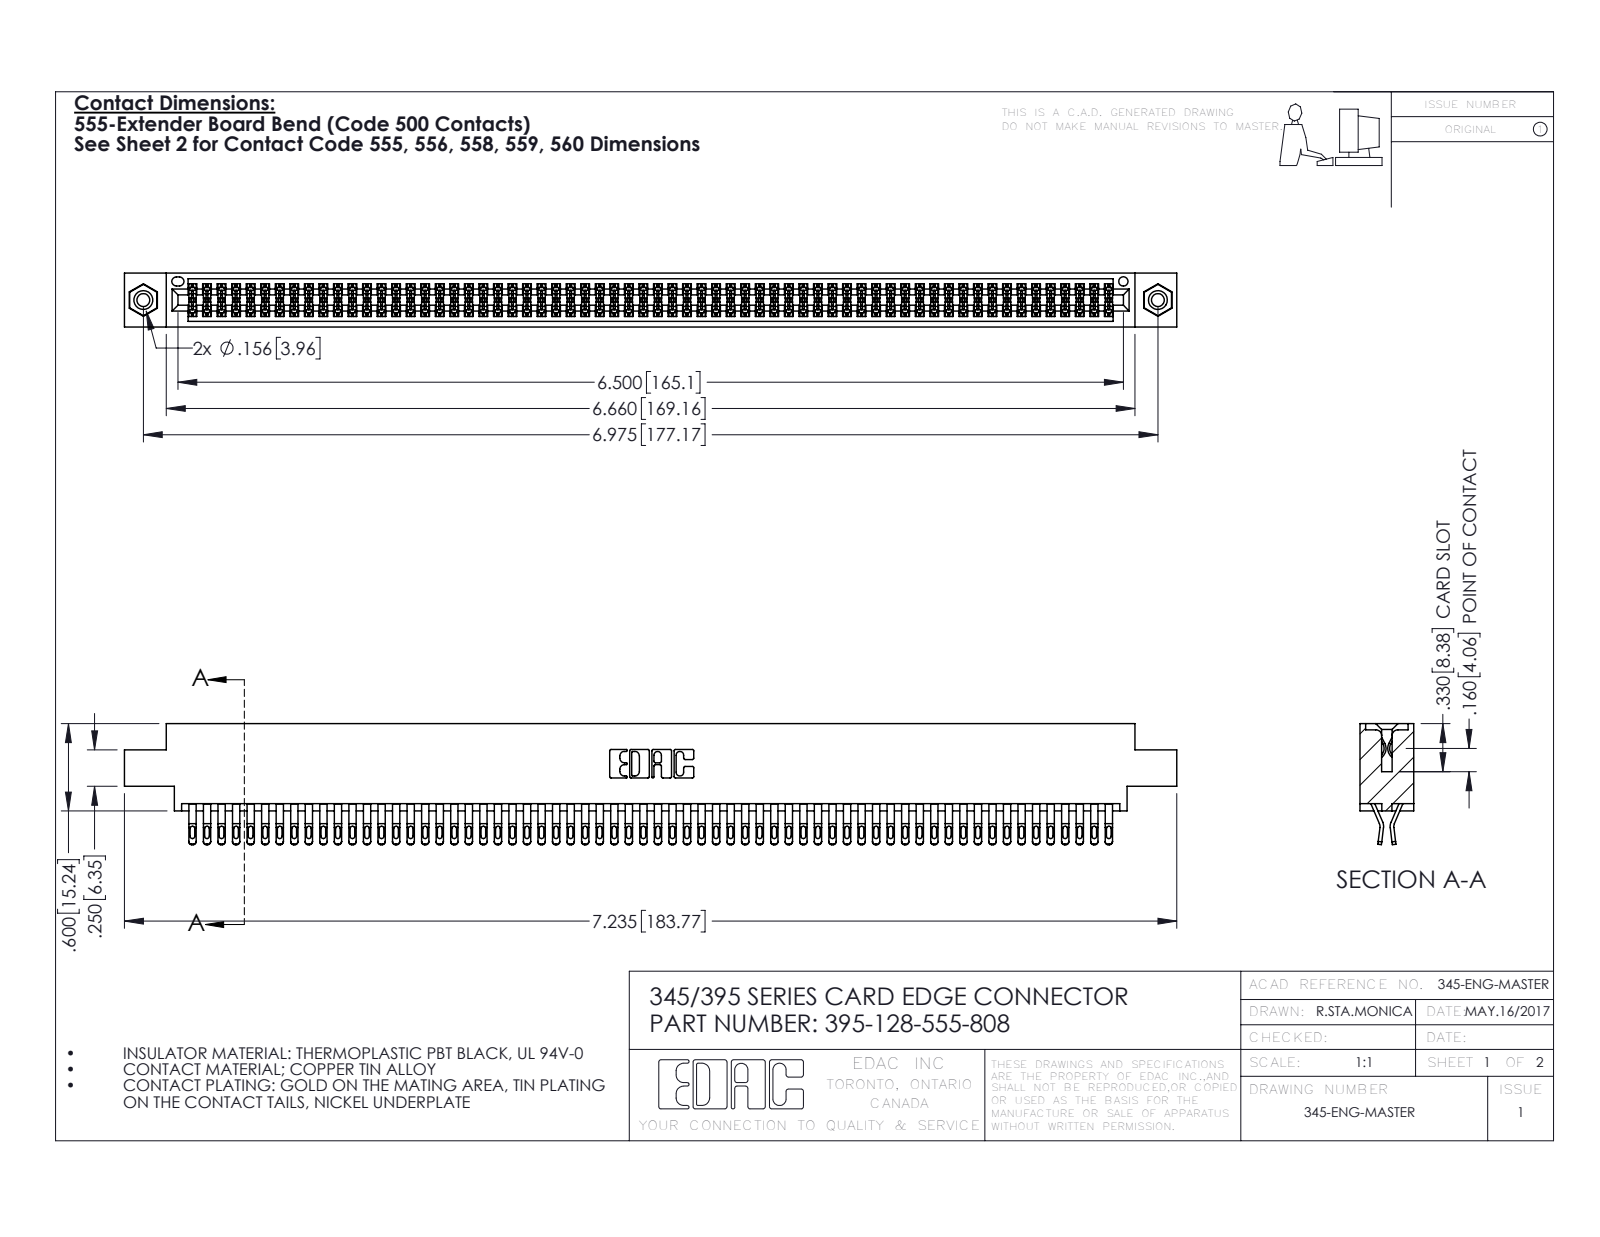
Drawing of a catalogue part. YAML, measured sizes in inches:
part_name: "345 Part_0.170 Offset - 0.156 Dia-TI; 395-128-555-808; 345-250-001_345-250-003-102; 345-292-001_555 Tail"
step_written_by: "SolidWorks 2016 (CONFIG_CONTROL_DESIGN)"
units: inches
bodies: {solids: 131, faces: 7358, planar: 4084, cylindrical: 3258, other: 16}
overall_size: [7.235, 0.832, 0.37]
volume: 1.117
surface_area: 44.85
round_holes:
  - {diameter: 0.089, count: 2}
  - {diameter: 0.125, count: 2}
  - {diameter: 0.156, count: 2}
  - {diameter: 0.064, count: 1}
round_bosses_or_shafts:
  - {diameter: 0.155, count: 2}
partial_cylinders:
  - {radius: 0.016, count: 320}
  - {radius: 0.02, count: 256}
  - {radius: 0.006, count: 192}
  - {radius: 0.01, count: 22}
  - {radius: 0.007, count: 6}
  - {radius: 0.031, count: 6}
  - {radius: 0.026, count: 3}
  - {radius: 0.01, count: 2}
face_to_face_distances: [0.072, 0.298, 0.025, 0.37, 0.2, 0.098, 0.272, 0.225, 0.175, 0.149]
hole_center_spacings: [0.27, 6.739, 6.975]
